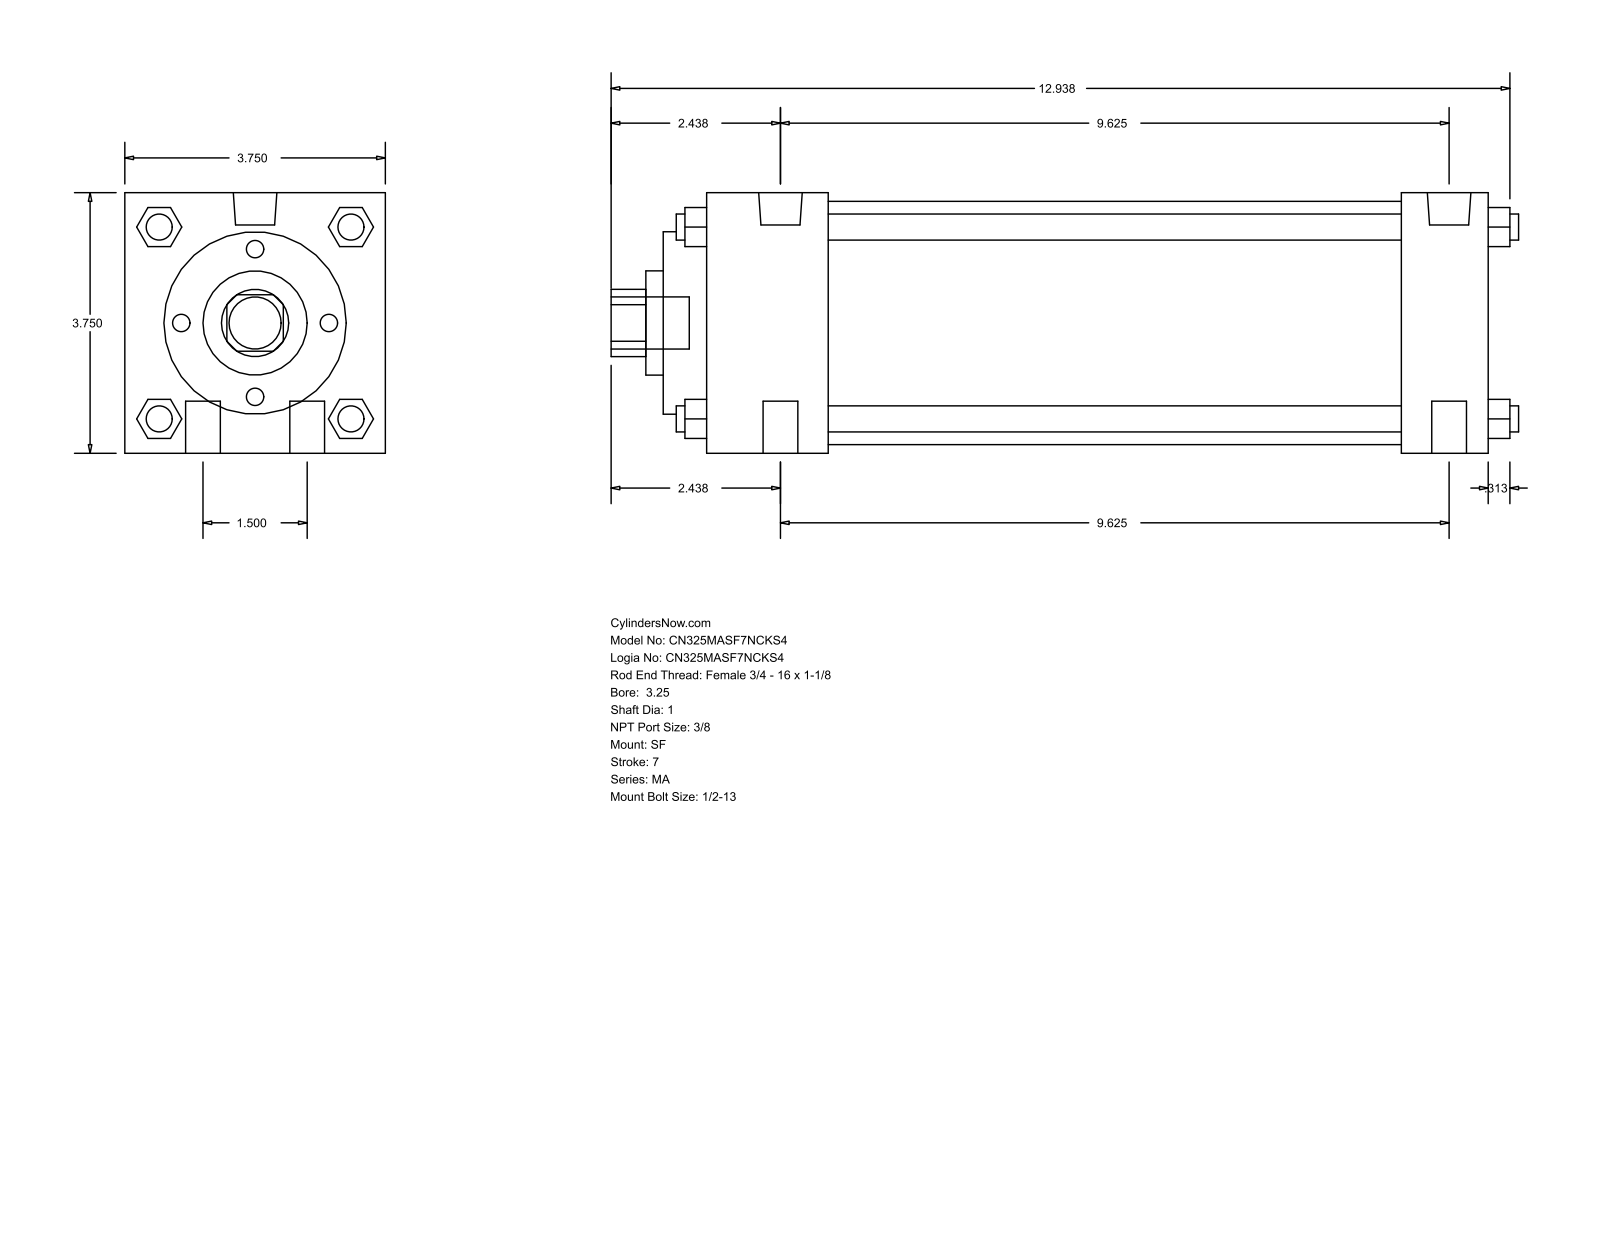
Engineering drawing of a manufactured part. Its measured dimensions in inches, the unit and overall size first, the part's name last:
Units: inches
Overall size (bounding box): 13.063 × 3.75 × 3.75
Round holes (diameter × count): ⌀1 ×1, ⌀1.5 ×1, ⌀2.625 ×1, ⌀3.5 ×1
Round bosses / shafts (diameter × count): ⌀0.5 ×4, ⌀0.375 ×4, ⌀0.627 ×2, ⌀0.437 ×2, ⌀0.75 ×1
Partial cylindrical surfaces — rounded edges, fillets, slot ends (radius × count): R0.484 ×1
Main face-to-face distances: 3.75, 11.25, 0.625, 10, 1.25, 1.75, 8.25, 9.5, 2.375, 10.625
Bodies: 0 solids, 126 faces (95 planar, 31 cylindrical, 0 other)
Part name (STEP PRODUCT): MA_SF__0325_1
STEP written by: GSSL Pune (CONFIG_CONTROL_DESIGN)
